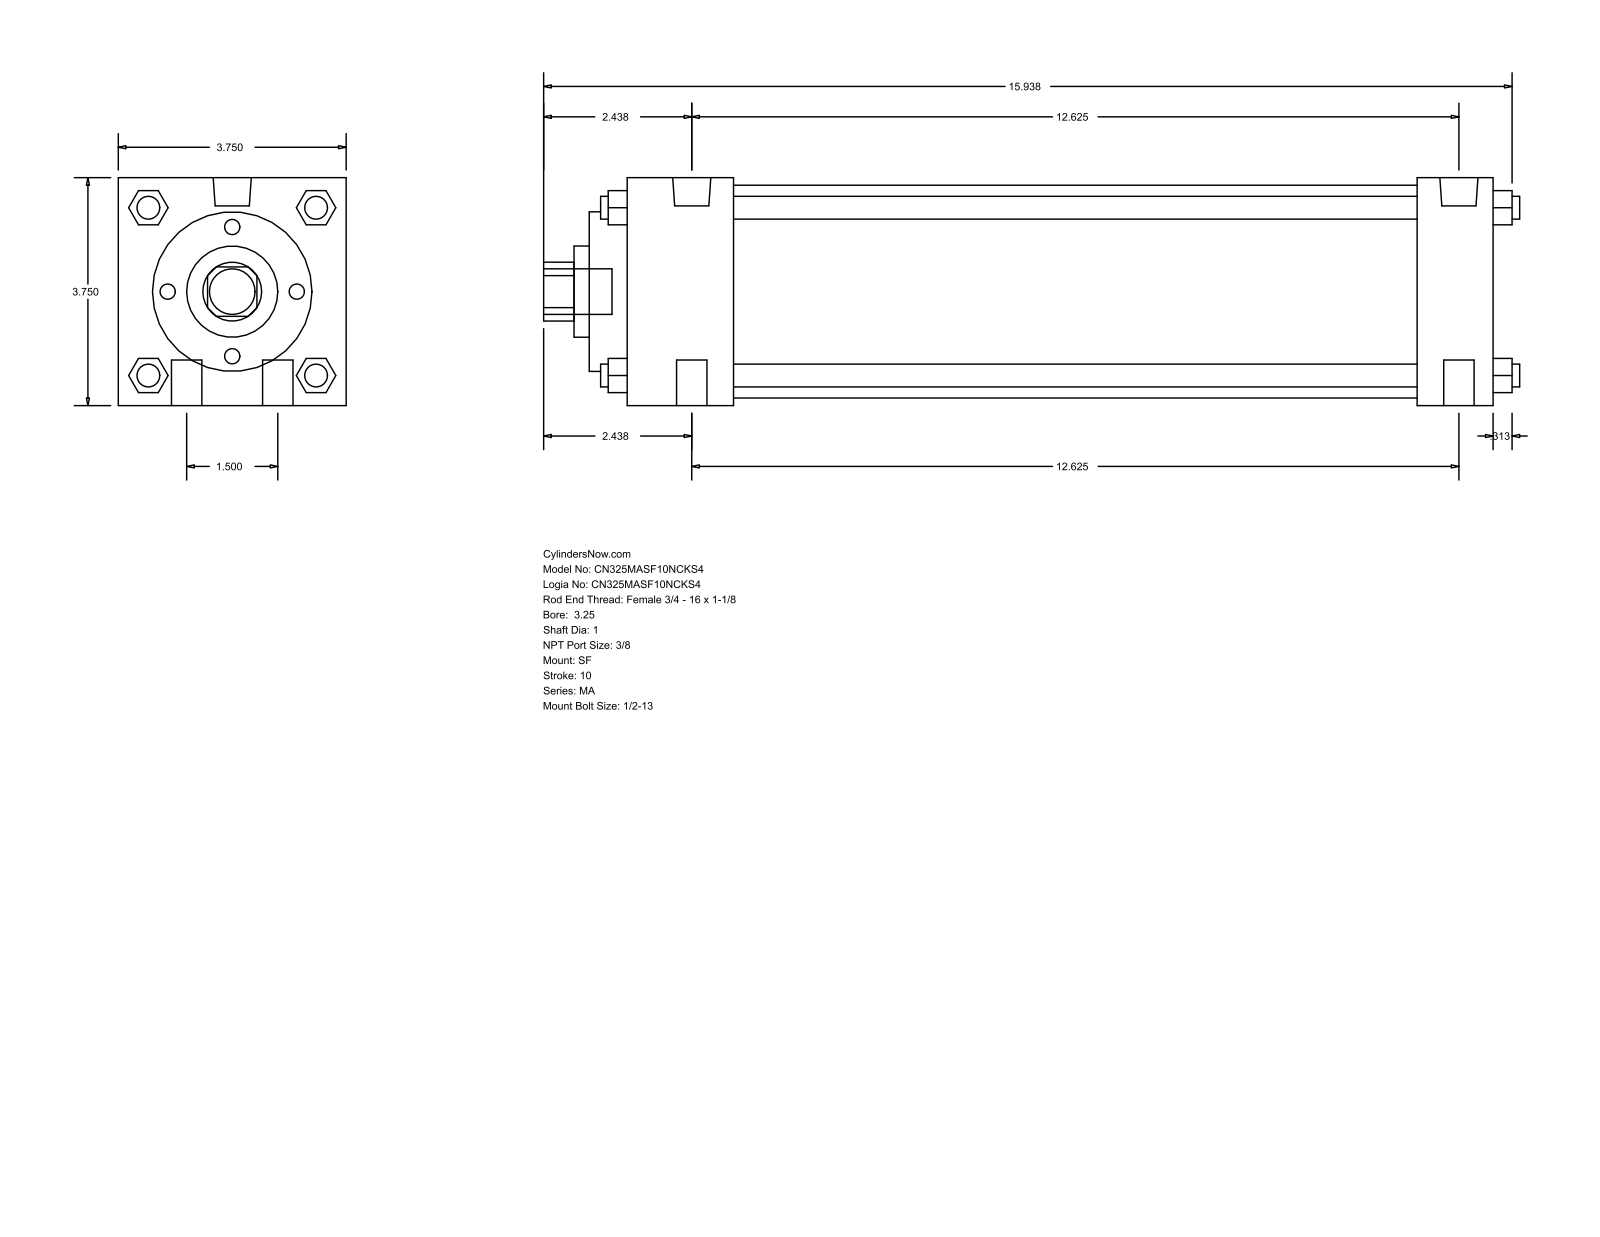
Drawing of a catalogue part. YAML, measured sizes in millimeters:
part_name: "MA_SF__0325_1"
step_written_by: "GSSL Pune (CONFIG_CONTROL_DESIGN)"
units: millimeters
bodies: {solids: 0, faces: 126, planar: 95, cylindrical: 31, other: 0}
overall_size: [407.99, 95.25, 95.25]
round_holes:
  - {diameter: 25.4, count: 1}
  - {diameter: 38.1, count: 1}
  - {diameter: 66.67, count: 1}
  - {diameter: 88.9, count: 1}
round_bosses_or_shafts:
  - {diameter: 12.7, count: 4}
  - {diameter: 9.53, count: 4}
  - {diameter: 15.93, count: 2}
  - {diameter: 11.11, count: 2}
  - {diameter: 19.05, count: 1}
partial_cylinders:
  - {radius: 12.29, count: 1}
face_to_face_distances: [95.24, 361.96, 15.87, 330.2, 31.76, 44.46, 285.74, 317.5, 60.33, 346.07]
